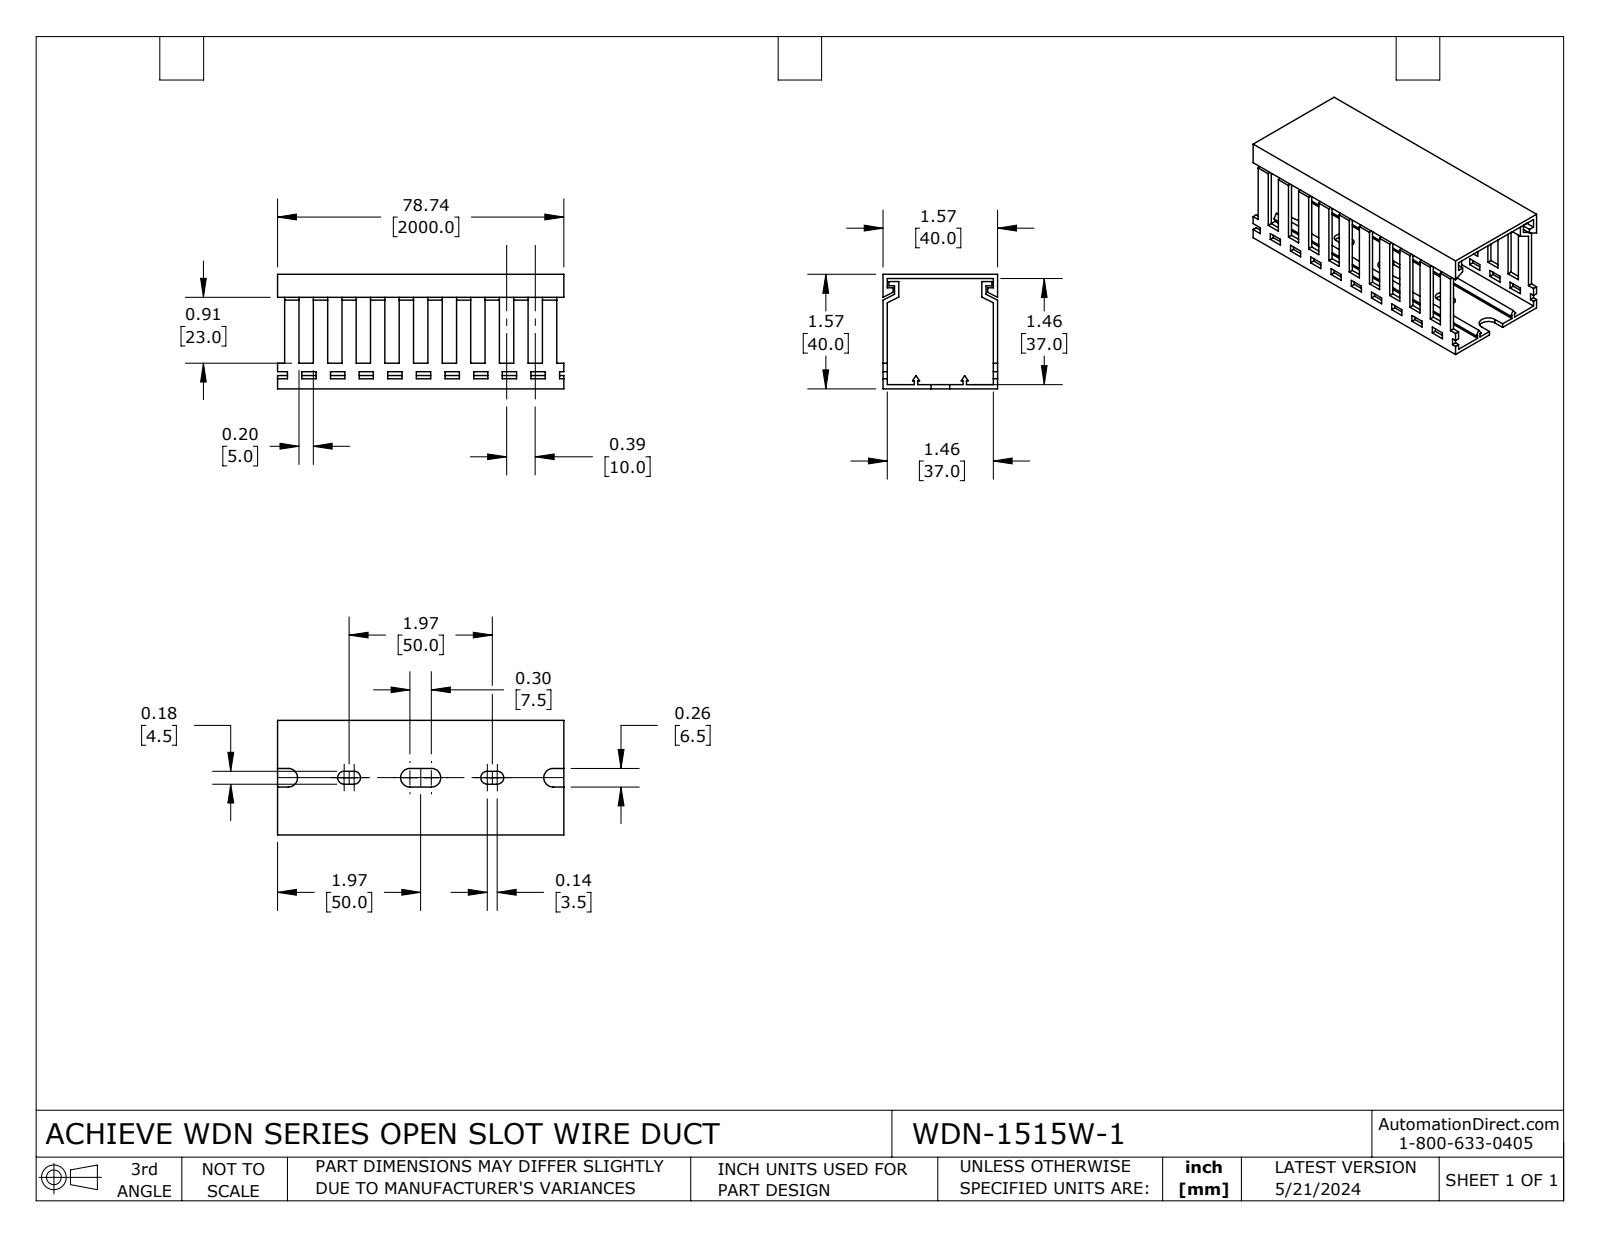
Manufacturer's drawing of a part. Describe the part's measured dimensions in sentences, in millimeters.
The part is named "WDN-1515W-1". Its 3-D file was written by "SolidWorks 2023 (CONFIG_CONTROL_DESIGN)". It is 2 solids with 350 faces: 338 planar, 12 cylindrical and 0 other. Overall it measures 100 by 40 by 40 millimeters. Its volume is 21 890 cubic millimeters and its surface area 32 720 square millimeters. Partial cylindrical surfaces (rounded edges, fillets, slot ends): 4 of radius 2.3, 4 of radius 3.3. The main face-to-face distances are 1.5, 38.5, 40, 37, 35, 10, 5, 15, 30, 20.
